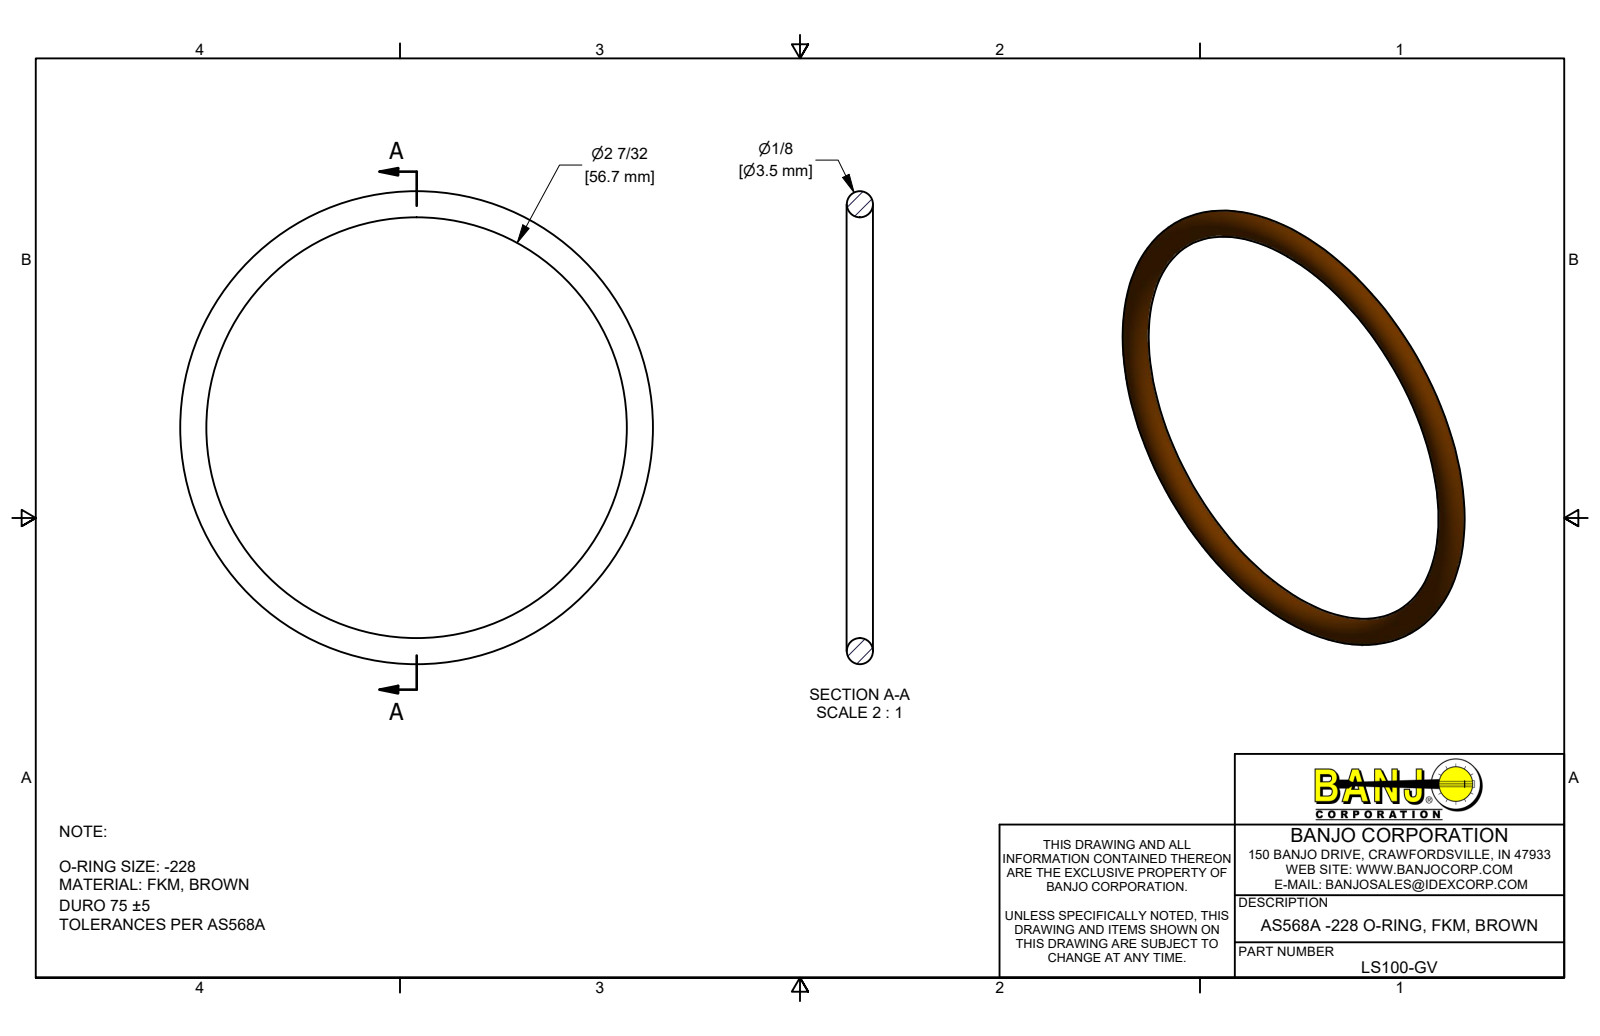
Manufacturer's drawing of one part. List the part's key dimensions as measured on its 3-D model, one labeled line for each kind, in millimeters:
Part name (STEP PRODUCT): LS100-GV
STEP written by: Autodesk Inventor 2019 (AUTOMOTIVE_DESIGN)
Units: millimetres
Bodies: 1 solid, 1 faces (0 planar, 0 cylindrical, 1 other)
Overall size (bounding box): 63.8 × 63.8 × 3.5
Volume: 1 850 mm³ · Surface area: 2 100 mm²
